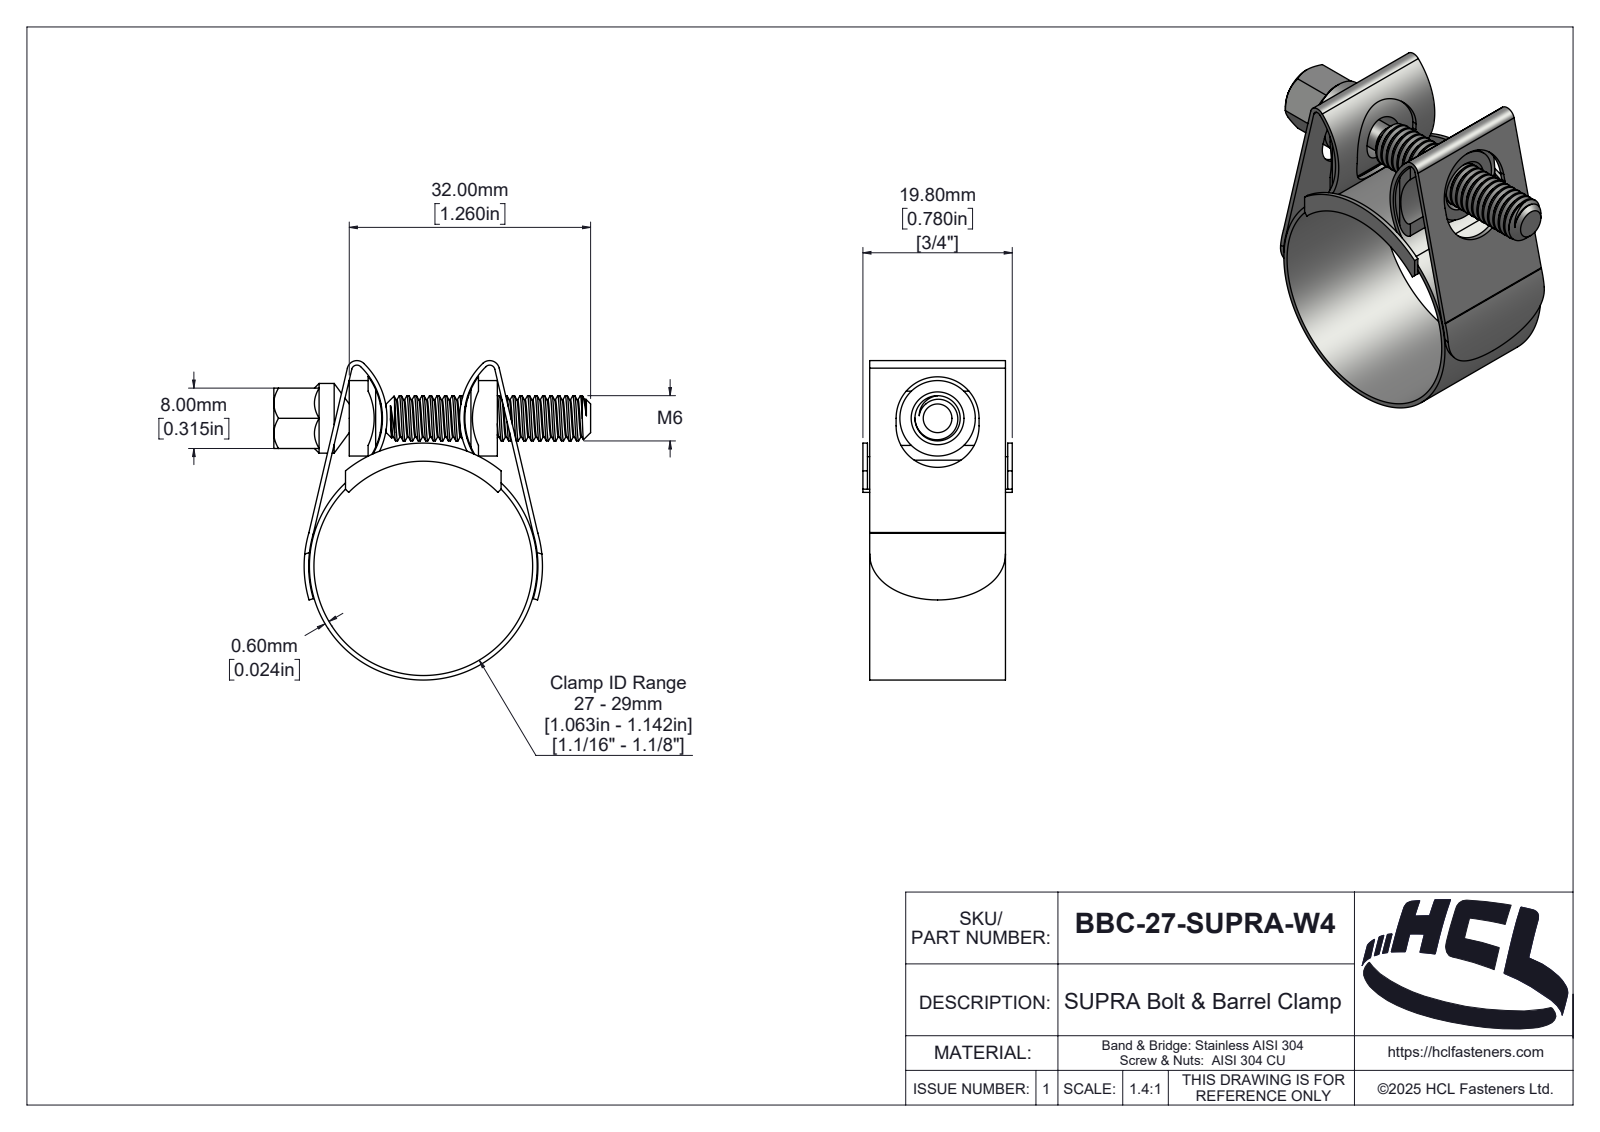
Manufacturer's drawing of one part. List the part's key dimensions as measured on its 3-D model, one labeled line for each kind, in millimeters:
Part name (STEP PRODUCT): BBC-27-SUPRA-W4
STEP written by: SolidWorks 2025 (AUTOMOTIVE_DESIGN)
Units: millimetres
Bodies: 5 solids, 288 faces (44 planar, 164 cylindrical, 80 other)
Overall size (bounding box): 42.33 × 42 × 19.8
Volume: 3 693 mm³ · Surface area: 8 933 mm²
Round holes (diameter × count): ⌀29 ×1
Round bosses / shafts (diameter × count): ⌀10 ×1, ⌀9.24 ×1, ⌀6 ×1, ⌀3.8 ×1
Partial cylindrical surfaces — rounded edges, fillets, slot ends (radius × count): R1 ×4, R0.7 ×2, R1.3 ×2, R2 ×2, R2.6 ×2, R5.5 ×2, R8.44 ×2, R9.44 ×2
Main face-to-face distances: 0.6, 18, 0.9, 18.9, 19.2, 18.3, 2.5, 17.14, 8, 18.6
